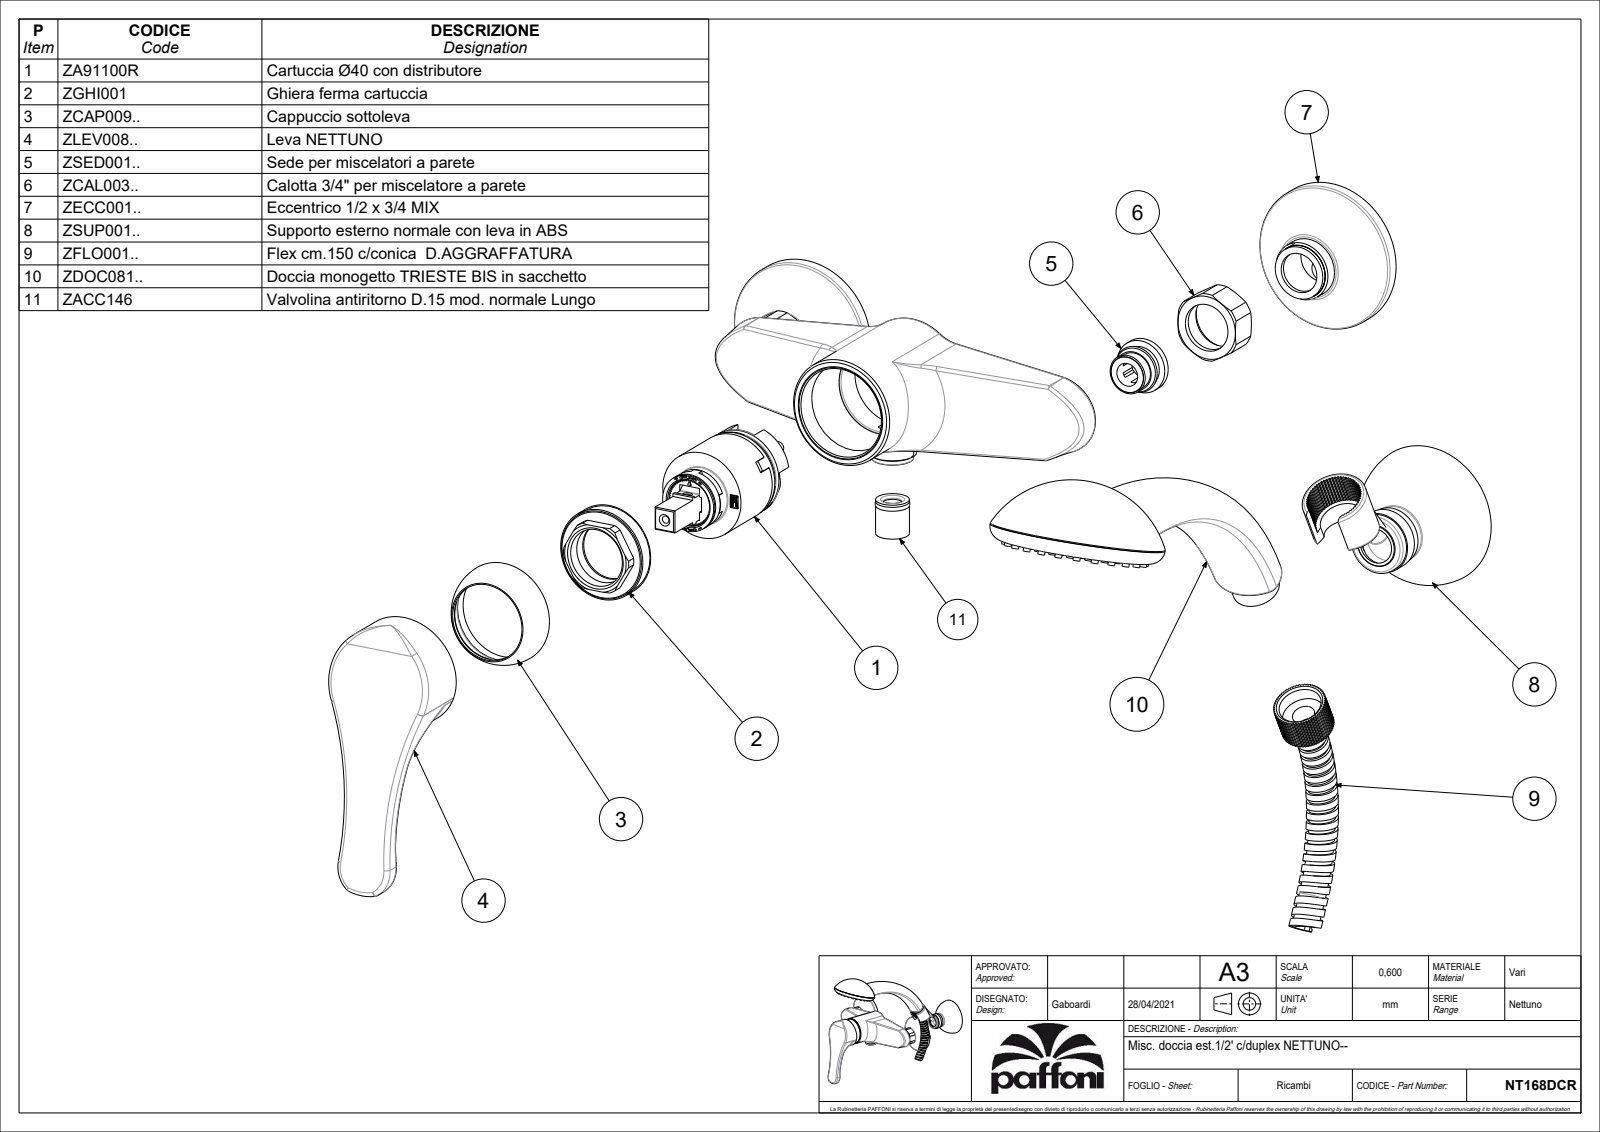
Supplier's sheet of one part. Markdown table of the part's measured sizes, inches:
| quantity | value |
| --- | --- |
| part name | NT168DCR |
| STEP written by | CREO PARAMETRIC BY PTC INC, 2020044 (CONFIG_CONTROL_DESIGN) |
| units | inches |
| bodies | 7 solids, 2557 faces (1027 planar, 632 cylindrical, 898 other) |
| overall size | 12.558 × 11.978 × 10.53 |
| volume | 22.61 in³ |
| surface area | 344.4 in² |
| round holes (diameter × count) | 0.315 × 4, 0.591 × 3, 0.709 × 3, 0.748 × 3, 0.177 × 2, 0.236 × 2, 0.276 × 2, 0.413 × 2, 0.472 × 2, 0.65 × 2, 0.827 × 2, 0.846 × 2 |
| round bosses / shafts (diameter × count) | 2.579 × 2, 1.115 × 2, 0.945 × 2, 0.728 × 2, 0.626 × 2, 0.37 × 2, 2.972 × 1, 2.854 × 1 |
| partial cylindrical surfaces (radius × count) | 0.02 × 63, 0.008 × 24, 0.03 × 16, 0.039 × 5, 0.079 × 5, 0.012 × 4, 0.059 × 4, 0.61 × 3 |
| main face-to-face distances | 0.138, 0.295, 0.433, 0.197, 0.394, 0.492, 0.256, 0.039, 0.551, 0.591 |
| hole center spacings | 0.39, 0.079, 0.339, 0.347, 0.4, 0.413, 0.513, 0.551 |
